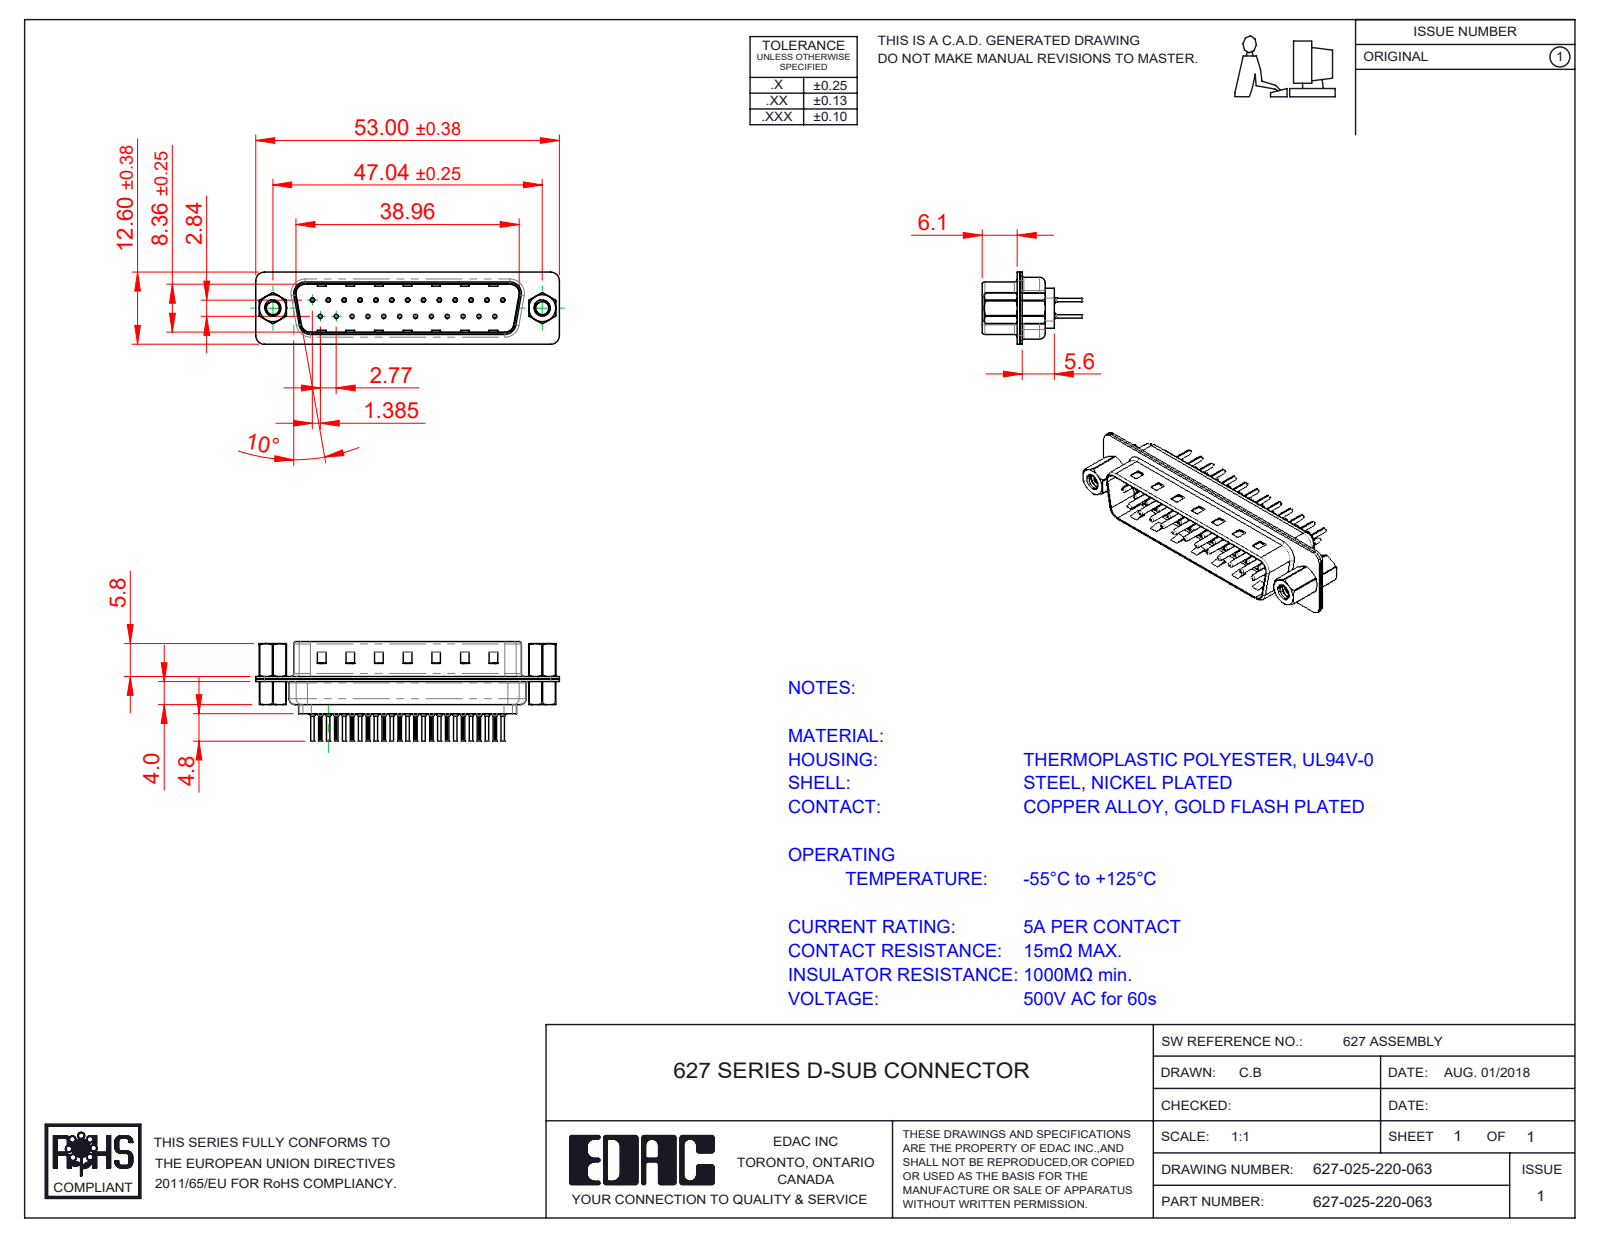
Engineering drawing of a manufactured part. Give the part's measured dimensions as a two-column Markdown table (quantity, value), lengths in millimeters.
| quantity | value |
| --- | --- |
| part name | 627-025-220-063; 627 Contact Row 1_20L; 627 4-40 Threaded Rivet; 627 4-40 Hex Standoff (+4 more) |
| STEP written by | SolidWorks 2020 (CONFIG_CONTROL_DESIGN) |
| units | millimeters |
| bodies | 32 solids, 2948 faces (793 planar, 1132 cylindrical, 1023 other) |
| overall size | 53 × 17.3 × 12.6 |
| volume | 2 890 mm³ |
| surface area | 8 277 mm² |
| round holes (diameter × count) | 0.2 × 25, 0.35 × 25, 1.1 × 25, 1.6 × 25, 2.26 × 2, 2.29 × 2, 4 × 2, 4.8 × 2 |
| round bosses / shafts (diameter × count) | 2 × 25, 1.5 × 25, 0.75 × 25, 0.6 × 25, 5 × 2, 4.9 × 2, 2.79 × 2 |
| partial cylindrical surfaces (radius × count) | 0.1 × 50, 1.5 × 16, 2 × 12, 0.5 × 8, 1.6 × 8, 0.25 × 4, 0.6 × 4, 0.65 × 4 |
| main face-to-face distances | 0.4, 0.45, 0.82, 9.58, 8.76, 0.9, 1.5, 1.4, 6.5, 6.05 |
| hole center spacings | 3.16, 8.31, 2.77, 5.54, 11.08, 16.62, 5.03, 5.04 |
